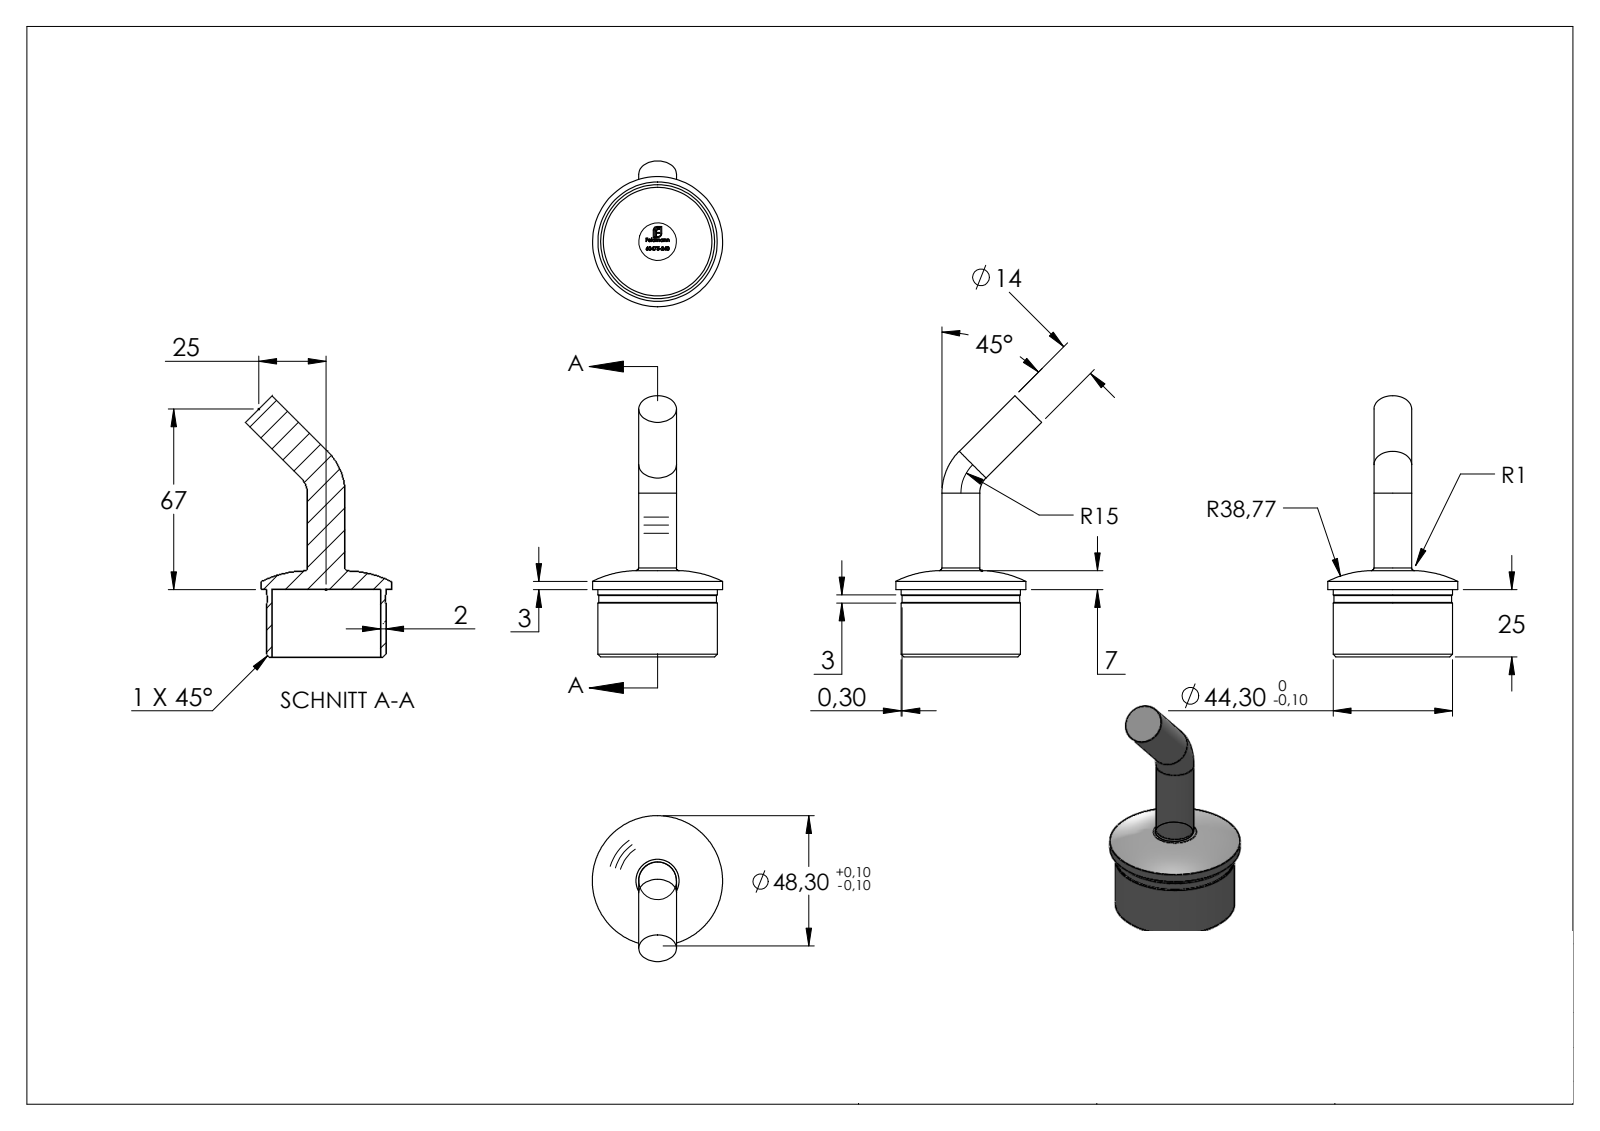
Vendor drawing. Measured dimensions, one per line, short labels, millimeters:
name: 60475-240
written by: SolidWorks 2018 (CONFIG_CONTROL_DESIGN)
unit: mm
bodies: 1 solid, 290 faces (154 planar, 14 cylindrical, 122 other)
size: 96.95 × 54.12 × 48.3
volume: 27 227 mm³; area: 13 857 mm²
holes: 1× ⌀40.3
bosses: 2× ⌀14, 1× ⌀48.3, 1× ⌀44.3, 1× ⌀43.7
face distances: 25, 25.1, 3, 2.1, 23, 2, 20, 5, 5.1, 0.31
